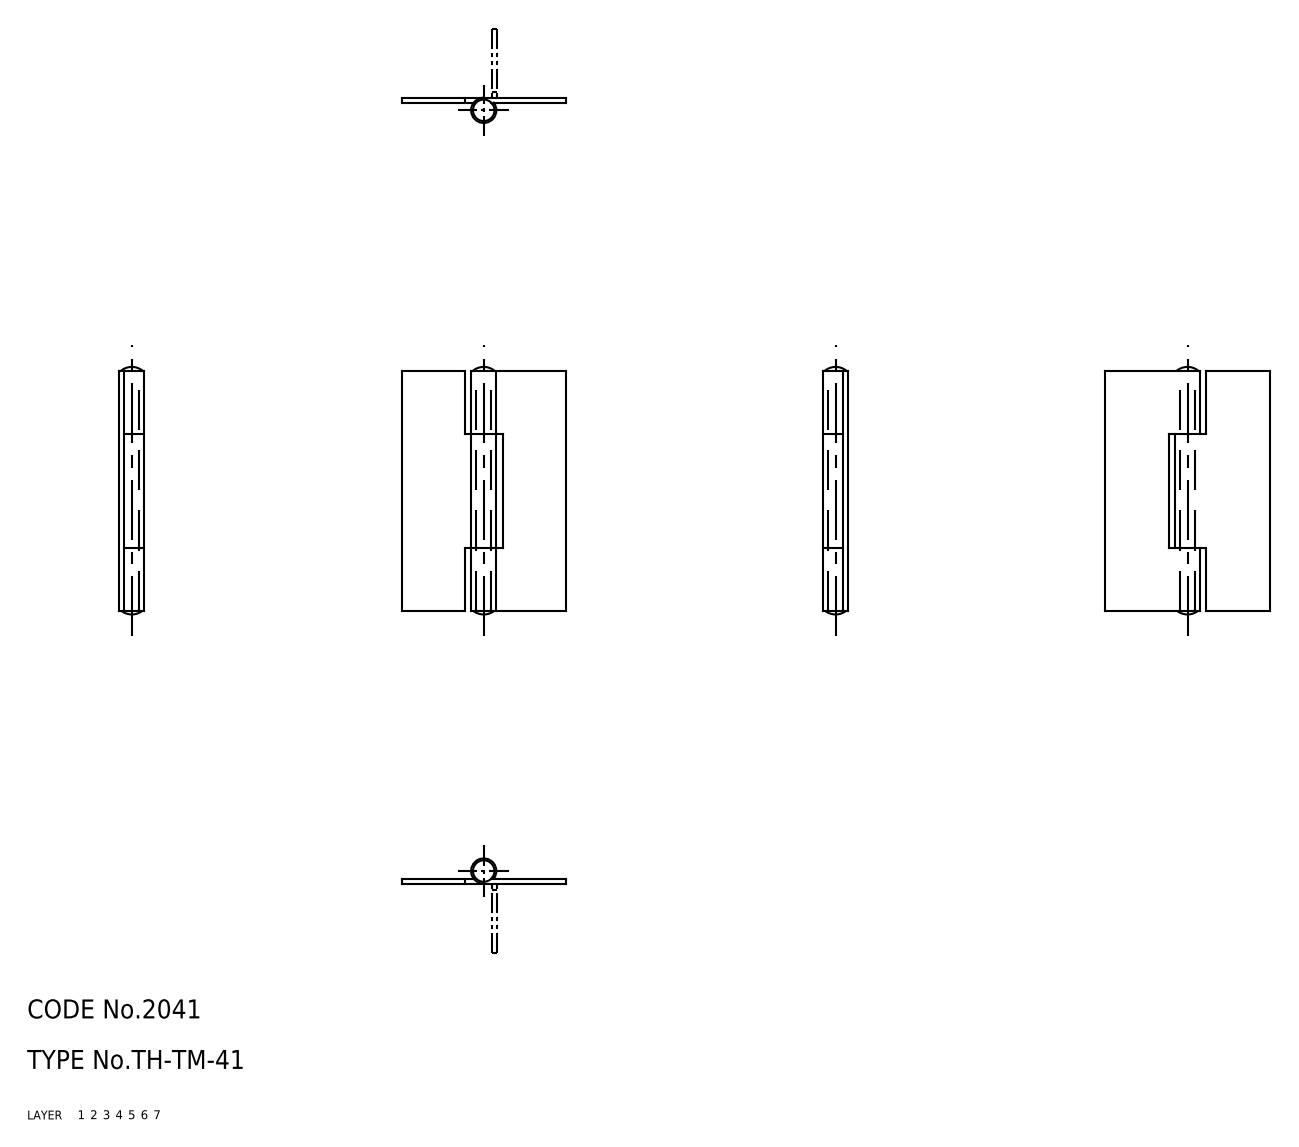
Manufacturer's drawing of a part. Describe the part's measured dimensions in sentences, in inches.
The part is named "67110374; 67110387; 67110400". Its 3-D file was written by "CADfix (AUTOMOTIVE_DESIGN)". It is 3 solids with 32 faces: 0 planar, 0 cylindrical and 32 other. Overall it measures 1.543 by 1.024 by 0.157 inches. Its volume is 0.069 cubic inches and its surface area 4.528 square inches.
